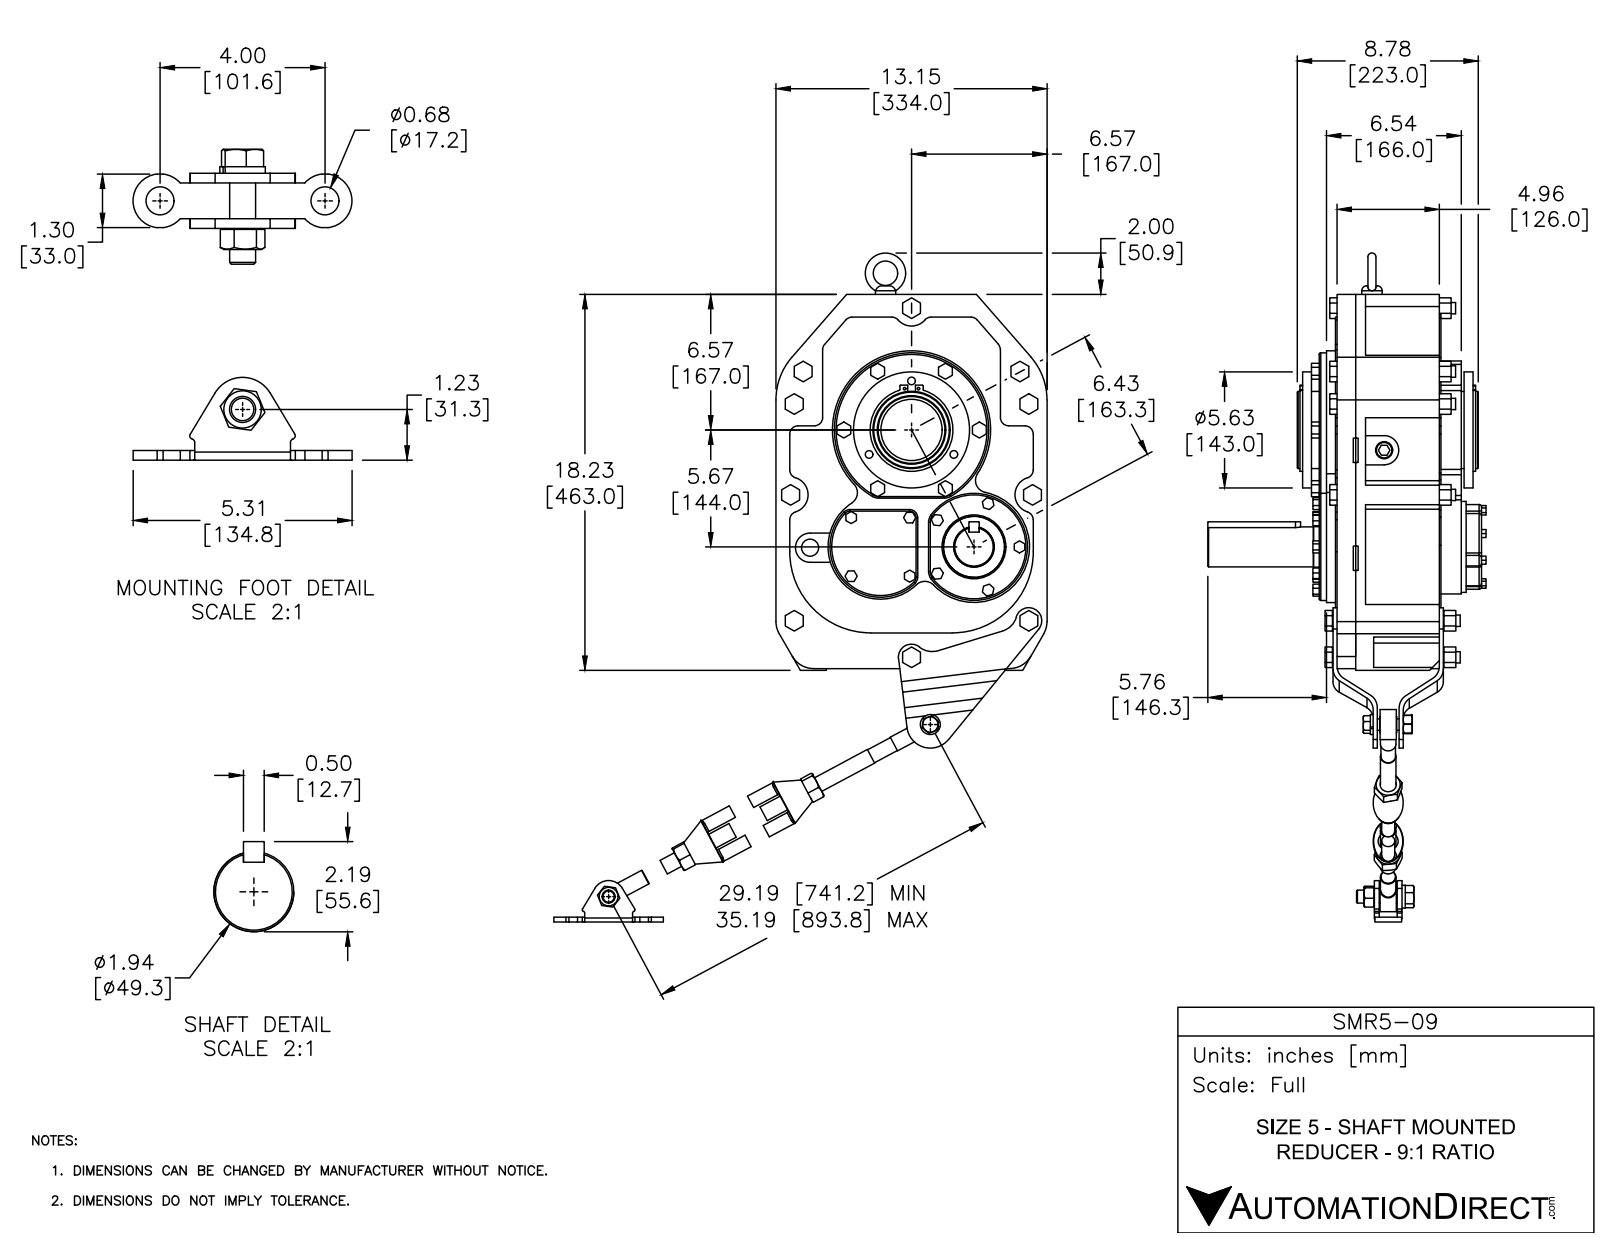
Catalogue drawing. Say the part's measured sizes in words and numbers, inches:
The part is named "SMR5-09; SMR5-09_REDUCER; SMR5-TA_4; SMR5-TA_2 (+4 more)". Its 3-D file was written by "SolidWorks 2016 (AUTOMOTIVE_DESIGN)". It is 74 solids with 1347 faces: 740 planar, 451 cylindrical and 156 other. Overall it measures 34.462 by 27.708 by 13.494 inches. Its volume is 1 200 cubic inches and its surface area 2 473 square inches. Round holes: 12 of diameter 0.591, 8 of diameter 0.531, 5 of diameter 0.827, 3 of diameter 0.368, 2 of diameter 0.118, 2 of diameter 0.677, 2 of diameter 0.689, 2 of diameter 0.787, 1 of diameter 0.551, 1 of diameter 0.559, 1 of diameter 0.571, 1 of diameter 0.63. Round bosses or shafts: 10 of diameter 0.551, 4 of diameter 0.75, 2 of diameter 1.457, 2 of diameter 0.711, 2 of diameter 0.63, 1 of diameter 7.48, 1 of diameter 5.63, 1 of diameter 5.197. Partial cylindrical surfaces (rounded edges, fillets, slot ends): 31 of radius 0.394, 19 of radius 0.591, 12 of radius 0.118, 8 of radius 0.079, 5 of radius 0.866, 4 of radius 0.039, 4 of radius 0.276, 4 of radius 0.709. The main face-to-face distances are 0.984, 0.079, 5.118, 5.039, 1.417, 0.512, 0.433, 0.866, 6.024, 0.906. The hole center spacings are 3.661, 5.178, 2.374, 2.984, 4.112, 10.512, 0.503, 1.5.
